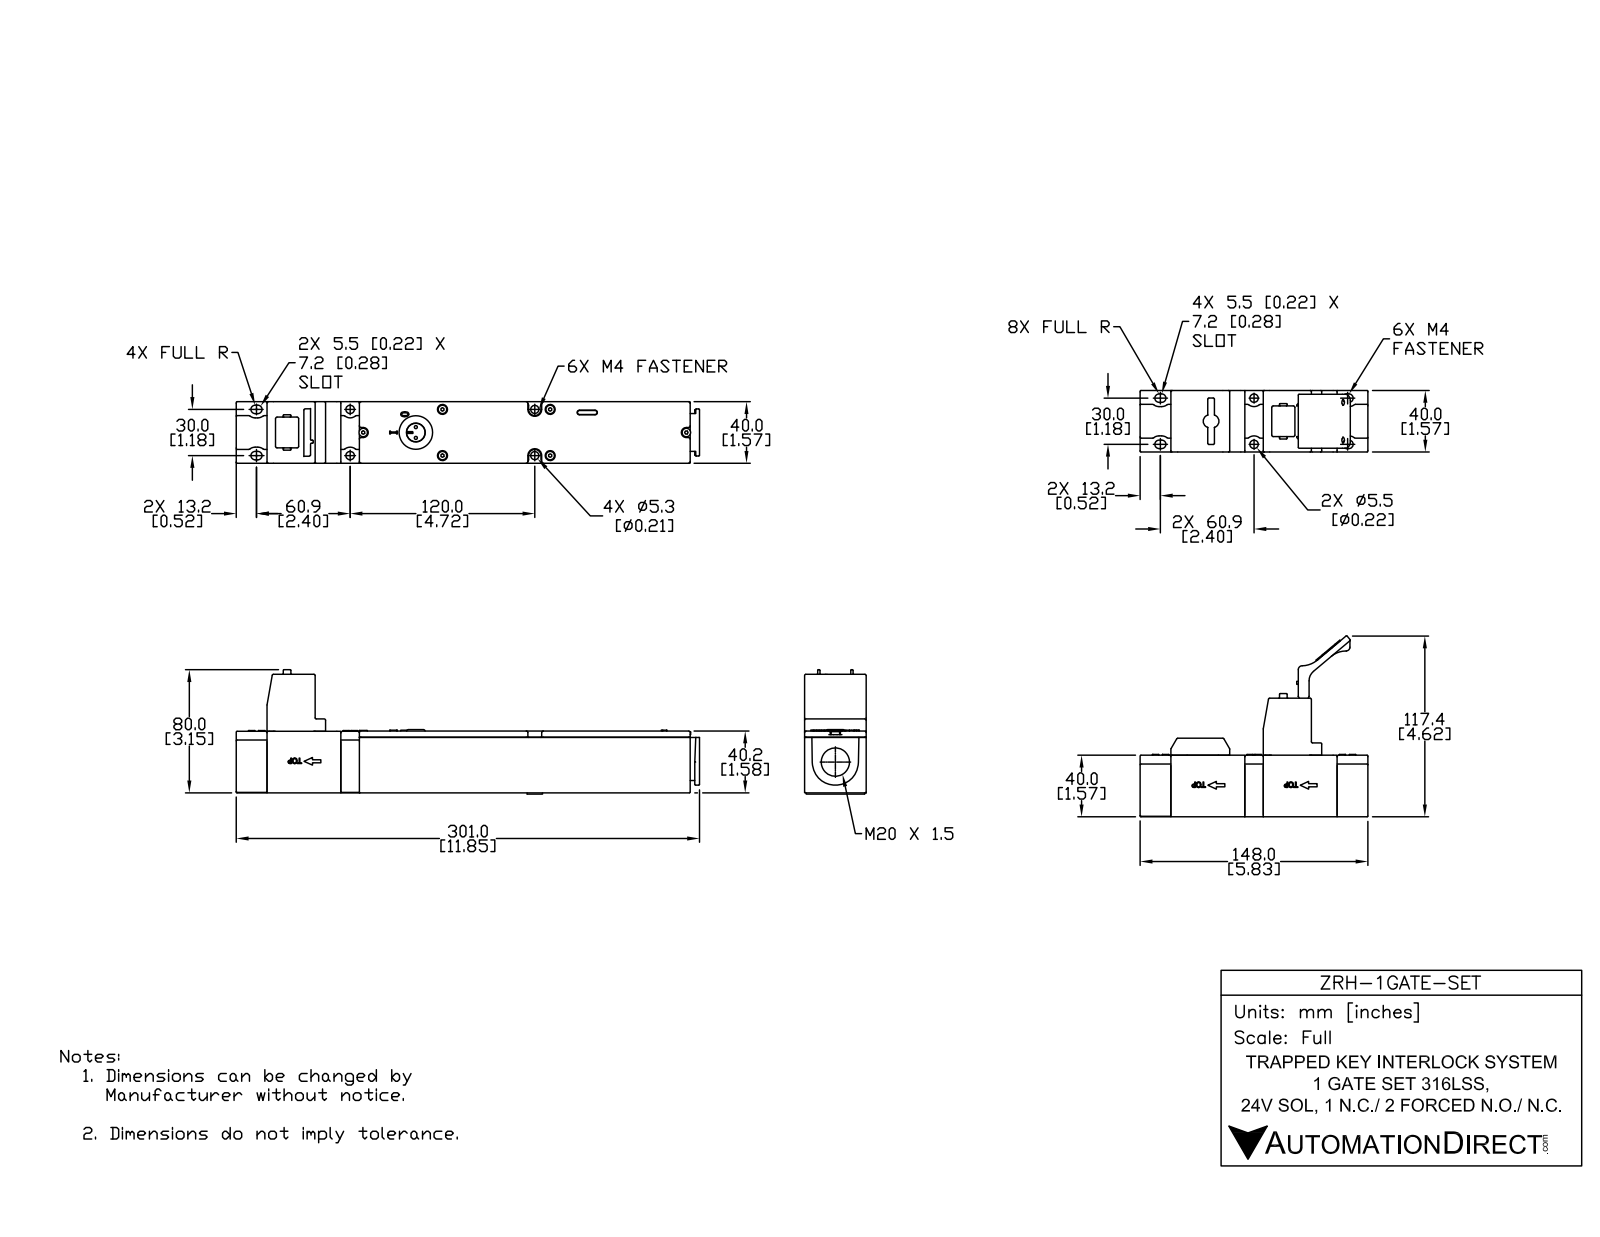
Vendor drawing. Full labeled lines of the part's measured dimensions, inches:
Part name (STEP PRODUCT): ST2130_01; ZRH-1GATE-SET; ST2323_STS-Schluessel_mit_Kodierung_NEU; ST2131_10 (+4 more)
STEP written by: SolidWorks 2017 (AUTOMOTIVE_DESIGN)
Units: inches
Bodies: 17 solids, 5589 faces (2442 planar, 909 cylindrical, 2238 other)
Overall size (bounding box): 11.85 × 7.916 × 4.641
Volume: 49.88 in³ · Surface area: 222.5 in²
Round holes (diameter × count): ⌀0.157 ×9, ⌀0.13 ×6, ⌀0.079 ×4, ⌀0.217 ×4, ⌀0.256 ×4, ⌀0.097 ×3, ⌀0.236 ×3, ⌀0.209 ×2, ⌀0.079 ×1, ⌀0.097 ×1, ⌀0.134 ×1, ⌀0.374 ×1
Round bosses / shafts (diameter × count): ⌀0.217 ×6, ⌀0.118 ×6, ⌀0.394 ×2, ⌀0.472 ×1, ⌀0.276 ×1, ⌀0.228 ×1, ⌀0.161 ×1
Partial cylindrical surfaces — rounded edges, fillets, slot ends (radius × count): R0.02 ×325, R0.039 ×111, R0.03 ×66, R0.006 ×46, R0.079 ×37, R0.018 ×36, R0.059 ×18, R0.217 ×16
Main face-to-face distances: 1.575, 6.331, 6.024, 2.362, 1.89, 8.386, 1.614, 7.913, 0.472, 7.906
Hole centre spacings: 1.181, 0.571, 2.362, 8.739, 0.138, 0.394, 0.591, 0.71
